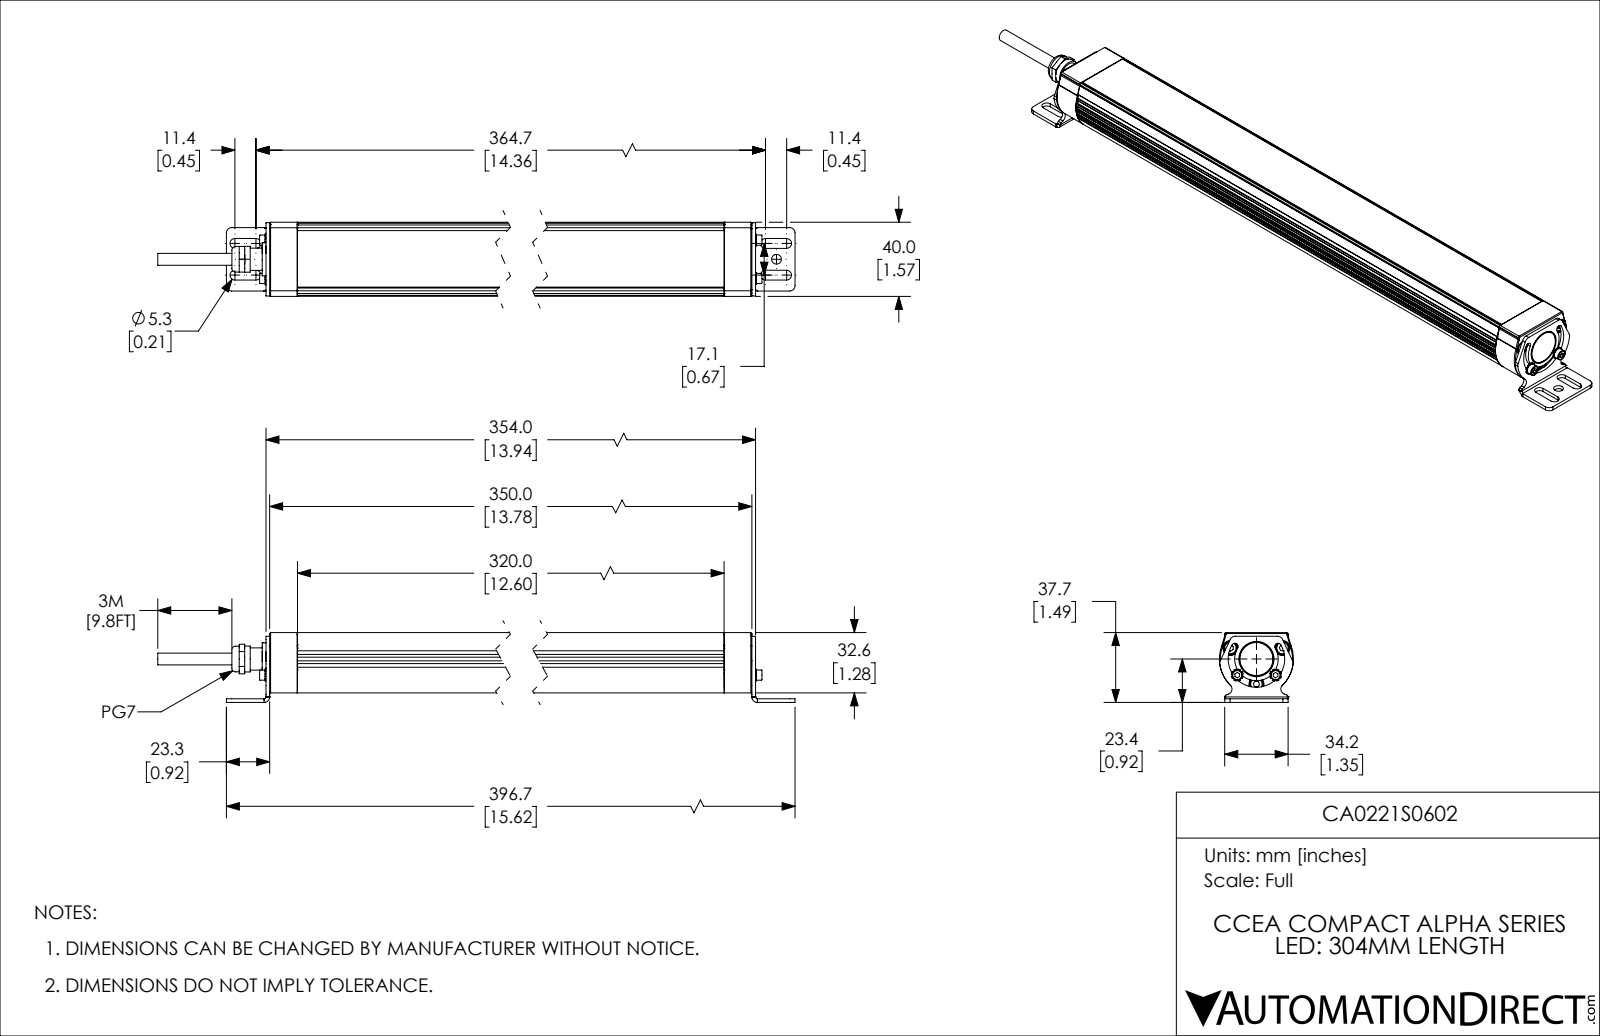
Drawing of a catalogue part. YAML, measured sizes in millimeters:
part_name: "CA0221S0602"
step_written_by: "SolidWorks 2021 (CONFIG_CONTROL_DESIGN)"
units: millimeters
bodies: {solids: 22, faces: 1182, planar: 392, cylindrical: 577, other: 213}
overall_size: [433.73, 40, 37.73]
volume: 194728
surface_area: 145856
round_holes:
  - {diameter: 2, count: 4}
  - {diameter: 3.3, count: 3}
  - {diameter: 4.5, count: 3}
  - {diameter: 7.5, count: 3}
  - {diameter: 2.5, count: 2}
  - {diameter: 3.2, count: 2}
  - {diameter: 5.3, count: 2}
  - {diameter: 8.5, count: 1}
  - {diameter: 11.5, count: 1}
  - {diameter: 12, count: 1}
  - {diameter: 14, count: 1}
  - {diameter: 19, count: 1}
round_bosses_or_shafts:
  - {diameter: 1, count: 4}
  - {diameter: 7, count: 3}
  - {diameter: 4, count: 3}
  - {diameter: 5.5, count: 2}
  - {diameter: 3, count: 2}
  - {diameter: 18.3, count: 1}
  - {diameter: 15, count: 1}
  - {diameter: 13.86, count: 1}
partial_cylinders:
  - {radius: 0.25, count: 56}
  - {radius: 1, count: 22}
  - {radius: 3, count: 22}
  - {radius: 2.65, count: 8}
  - {radius: 2.85, count: 6}
  - {radius: 5.5, count: 6}
  - {radius: 1.5, count: 4}
  - {radius: 0.3, count: 2}
face_to_face_distances: [2, 4.01, 0.5, 28.48, 32.49, 27.98, 4.51, 4, 2.5, 25.98]
hole_center_spacings: [13.5, 1, 4.68, 5.63, 11.41, 13.07, 13.16, 15.09]
